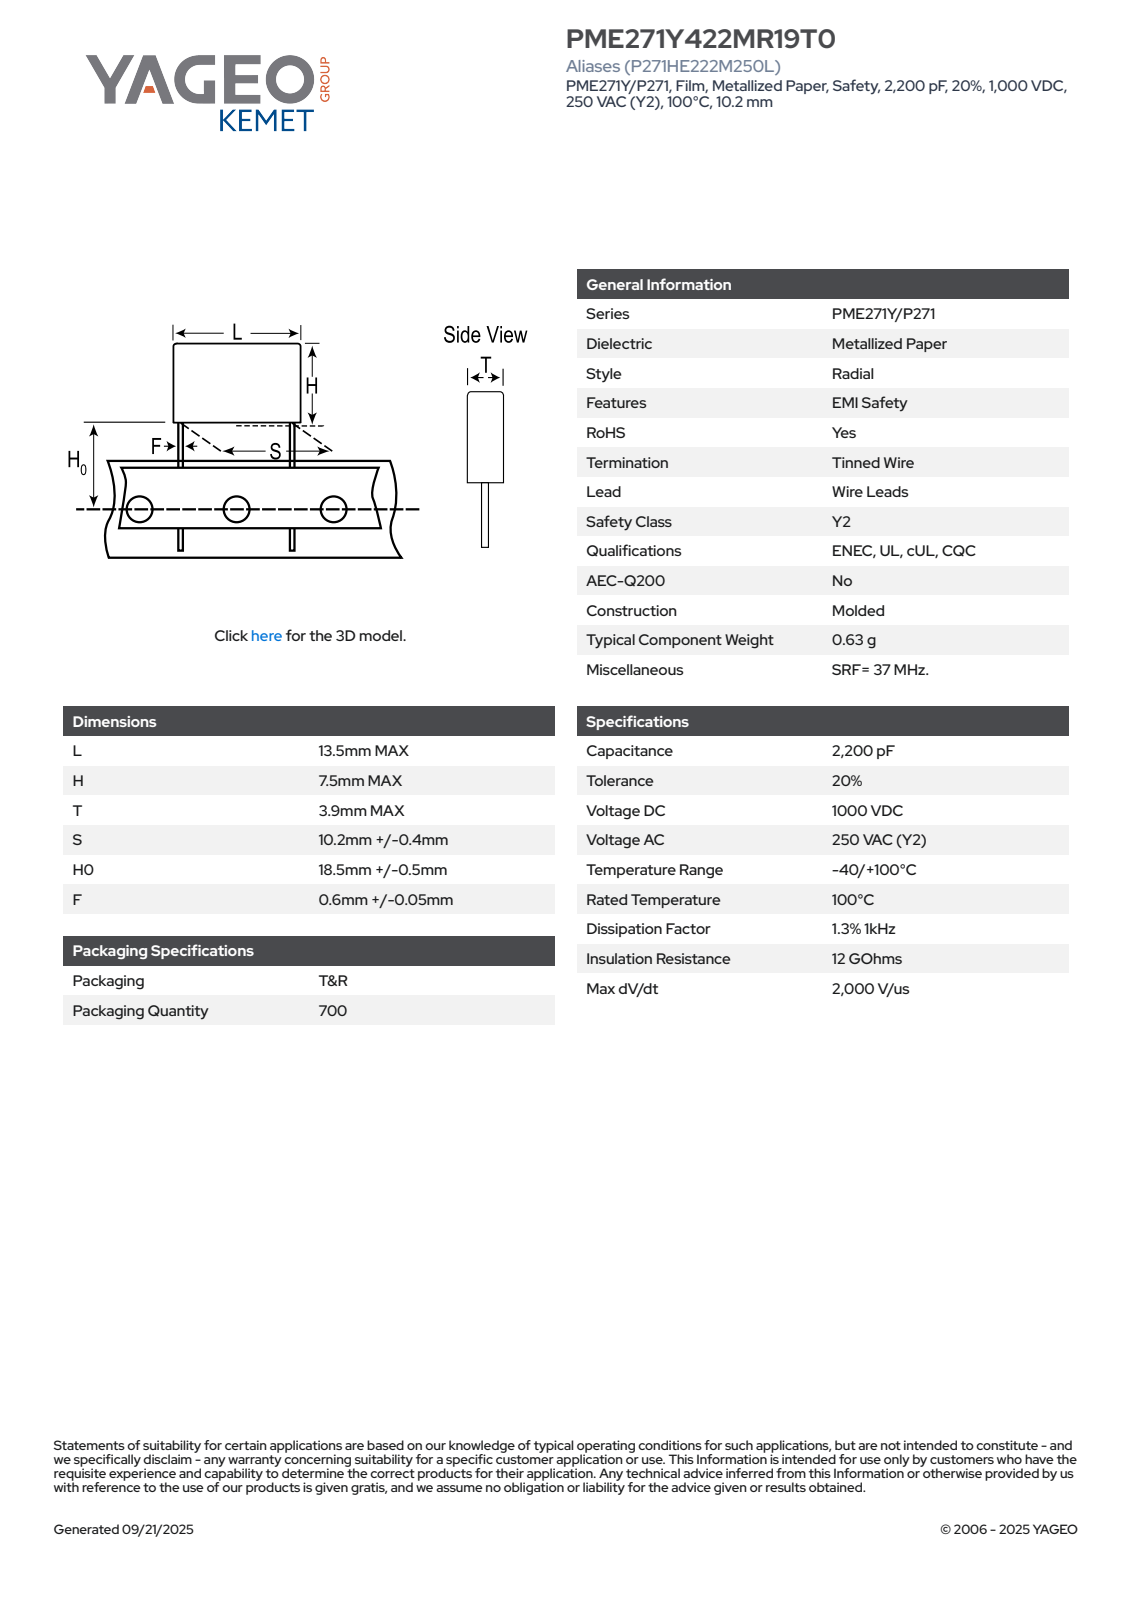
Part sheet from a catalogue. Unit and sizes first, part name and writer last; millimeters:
Units: millimetres
Overall size (bounding box): 26.5 × 13.5 × 3.9
Round bosses / shafts (diameter × count): ⌀0.65 ×2
Partial cylindrical surfaces — rounded edges, fillets, slot ends (radius × count): R0.5 ×4
Main face-to-face distances: 3.9, 7.5, 13.5, 19, 26.5, 1.21, 23.35, 4.35, 3.15, 22.14
Volume: 406 mm³ · Surface area: 445 mm²
Bodies: 4 solids, 73 faces (65 planar, 8 cylindrical, 0 other)
Part name (STEP PRODUCT): CFR_MOLDED_13.5X7.5X3.9_L13.5H7.5T3.9S10.2H019F0.65
STEP written by: SolidWorks 2014 (AUTOMOTIVE_DESIGN)
